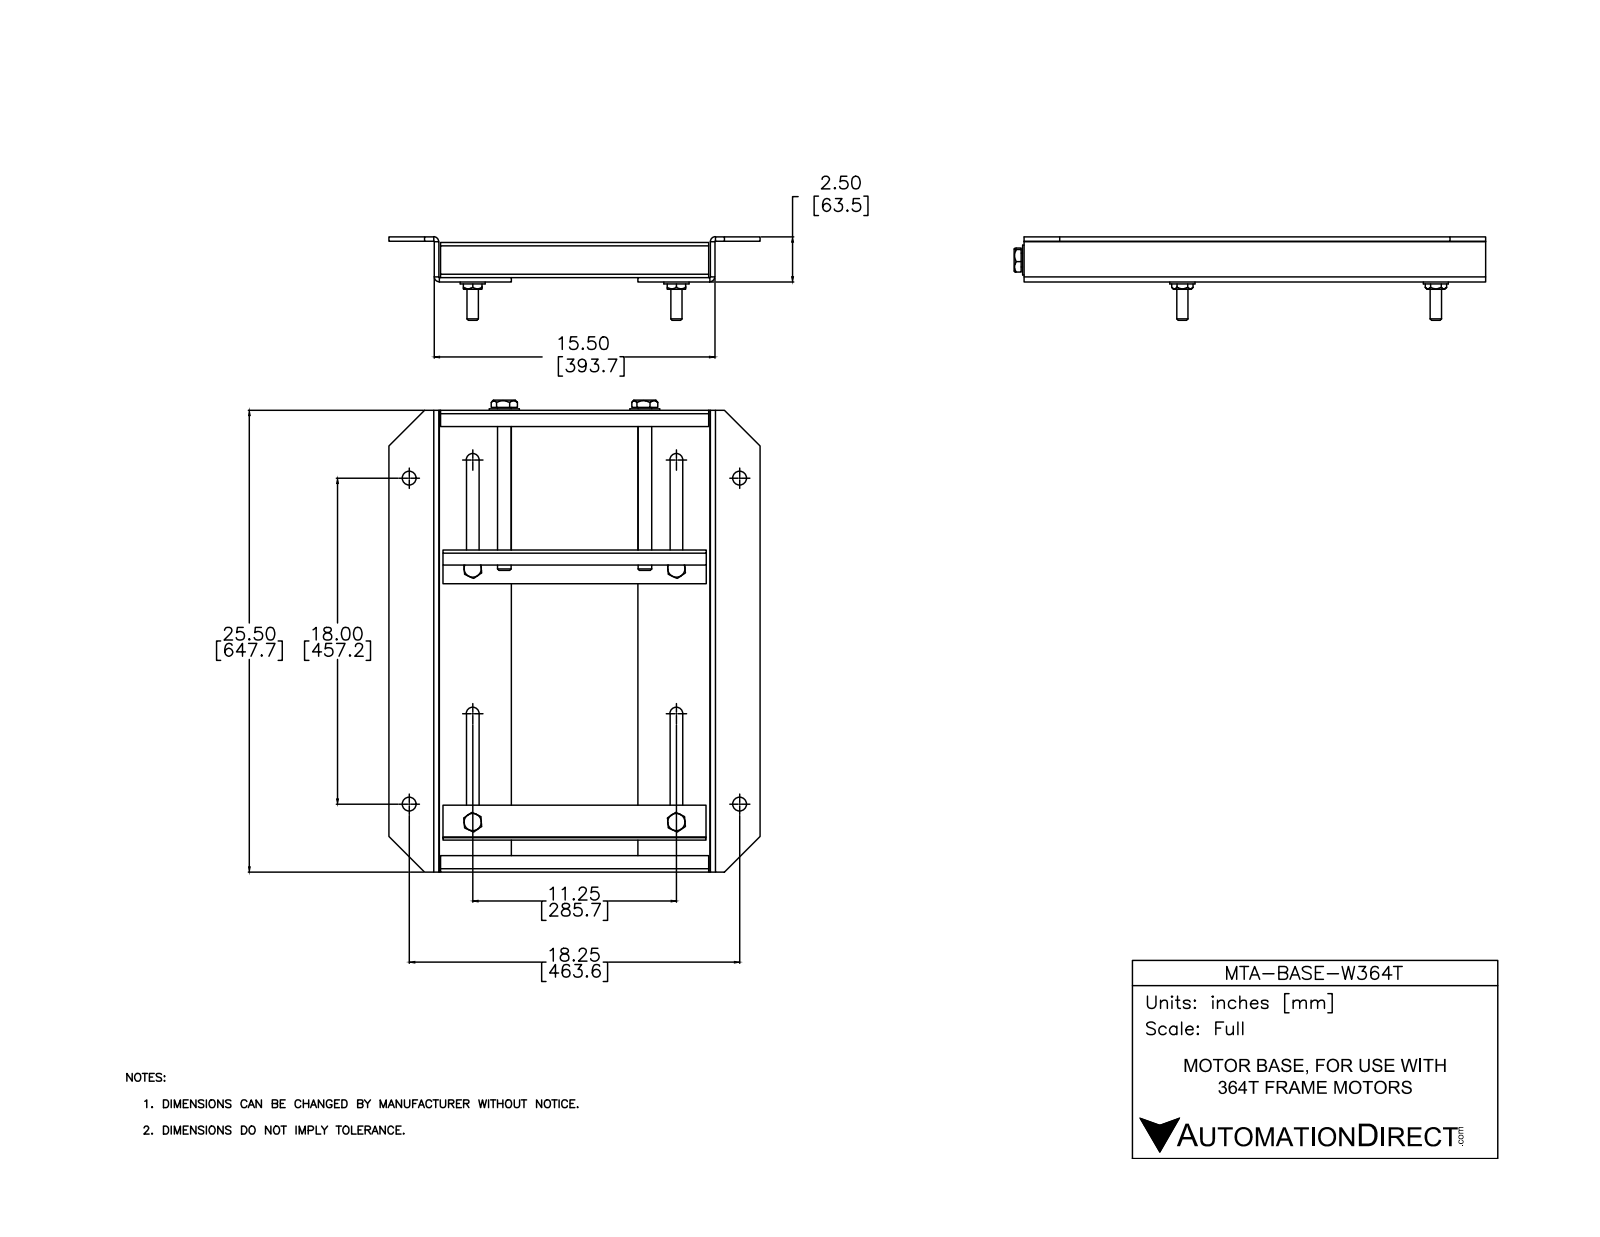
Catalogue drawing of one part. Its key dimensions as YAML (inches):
part_name: "W364T"
step_written_by: "SolidWorks 2017 (AUTOMOTIVE_DESIGN)"
units: inches
bodies: {solids: 26, faces: 410, planar: 224, cylindrical: 110, other: 76}
overall_size: [26.051, 20.5, 4.612]
volume: 153.6
surface_area: 1477
round_holes:
  - {diameter: 0.75, count: 6}
  - {diameter: 0.63, count: 4}
  - {diameter: 0.65, count: 4}
  - {diameter: 0.866, count: 4}
  - {diameter: 0.625, count: 2}
  - {diameter: 0.625, count: 2}
  - {diameter: 0.787, count: 2}
round_bosses_or_shafts:
  - {diameter: 1.386, count: 4}
  - {diameter: 1.654, count: 2}
partial_cylinders:
  - {radius: 0.029, count: 11}
  - {radius: 0.35, count: 8}
  - {radius: 0.186, count: 4}
  - {radius: 0.279, count: 4}
  - {radius: 0.167, count: 3}
face_to_face_distances: [0.25, 2.25, 2.5, 2, 0.138, 15.25, 0.157, 2.112, 0.388, 1.862]
hole_center_spacings: [14, 11.25, 7.756, 13.467, 13.467, 17.96, 18, 18.25]
